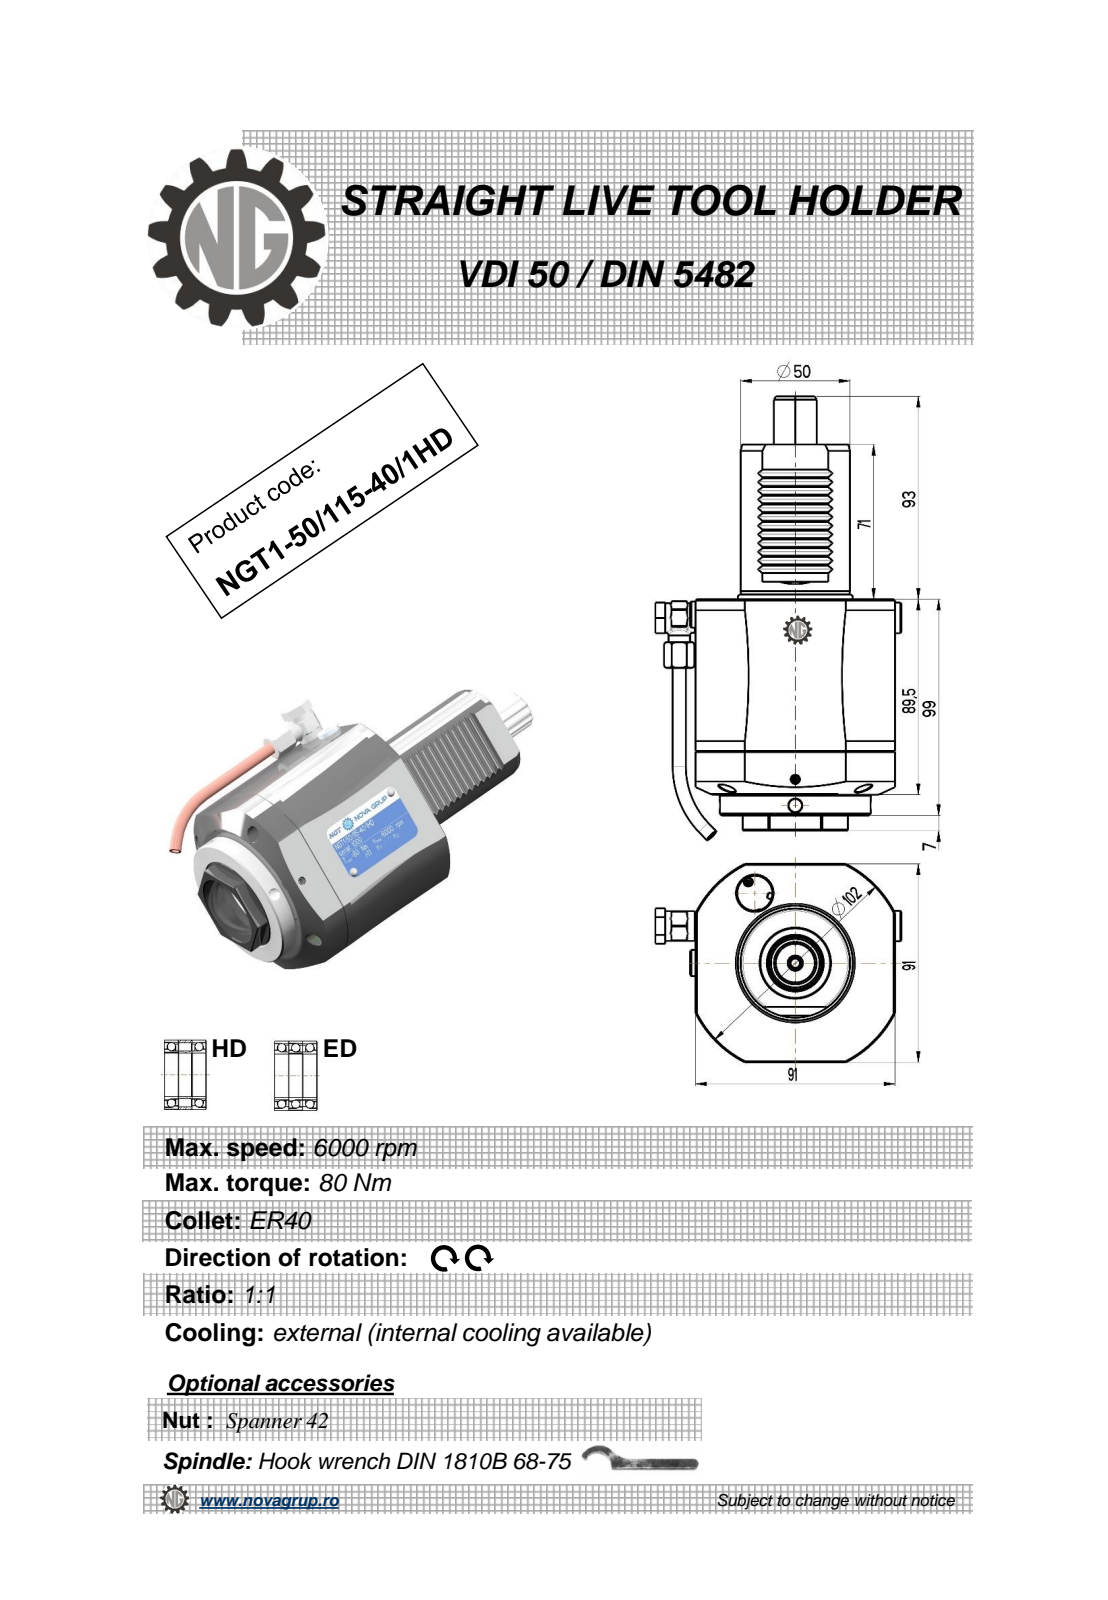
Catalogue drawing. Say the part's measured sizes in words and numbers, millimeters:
The part is named "NGT1_50_115_40_3HD". Its 3-D file was written by "PRO/ENGINEER BY PARAMETRIC TECHNOLOGY CORPORATION, 2010280 (CONFIG_CONTROL_DESIGN)". It is 1 solid with 433 faces: 141 planar, 154 cylindrical and 138 other. Overall it measures 203.44 by 112.4 by 91 millimeters. Its volume is 828 628 cubic millimeters and its surface area 66 971 square millimeters. Round holes: 3 of diameter 4, 2 of diameter 6, 1 of diameter 3, 1 of diameter 4.2, 1 of diameter 5.3, 1 of diameter 6.2, 1 of diameter 9, 1 of diameter 10, 1 of diameter 11, 1 of diameter 36.2, 1 of diameter 42. Round bosses or shafts: 2 of diameter 6, 1 of diameter 69, 1 of diameter 50, 1 of diameter 14, 1 of diameter 13.6, 1 of diameter 13, 1 of diameter 12, 1 of diameter 10. Partial cylindrical surfaces (rounded edges, fillets, slot ends): 24 of radius 3.33, 12 of radius 0.3, 6 of radius 0.41, 4 of radius 0.5, 2 of radius 20, 1 of radius 6.25, 1 of radius 7.7, 1 of radius 8.64. The main face-to-face distances are 91, 89.5, 9.5, 99, 170, 160.5, 71, 2.83, 14.14, 11.31. The hole center spacings are 0.4, 55.66, 56.04, 87.66.
